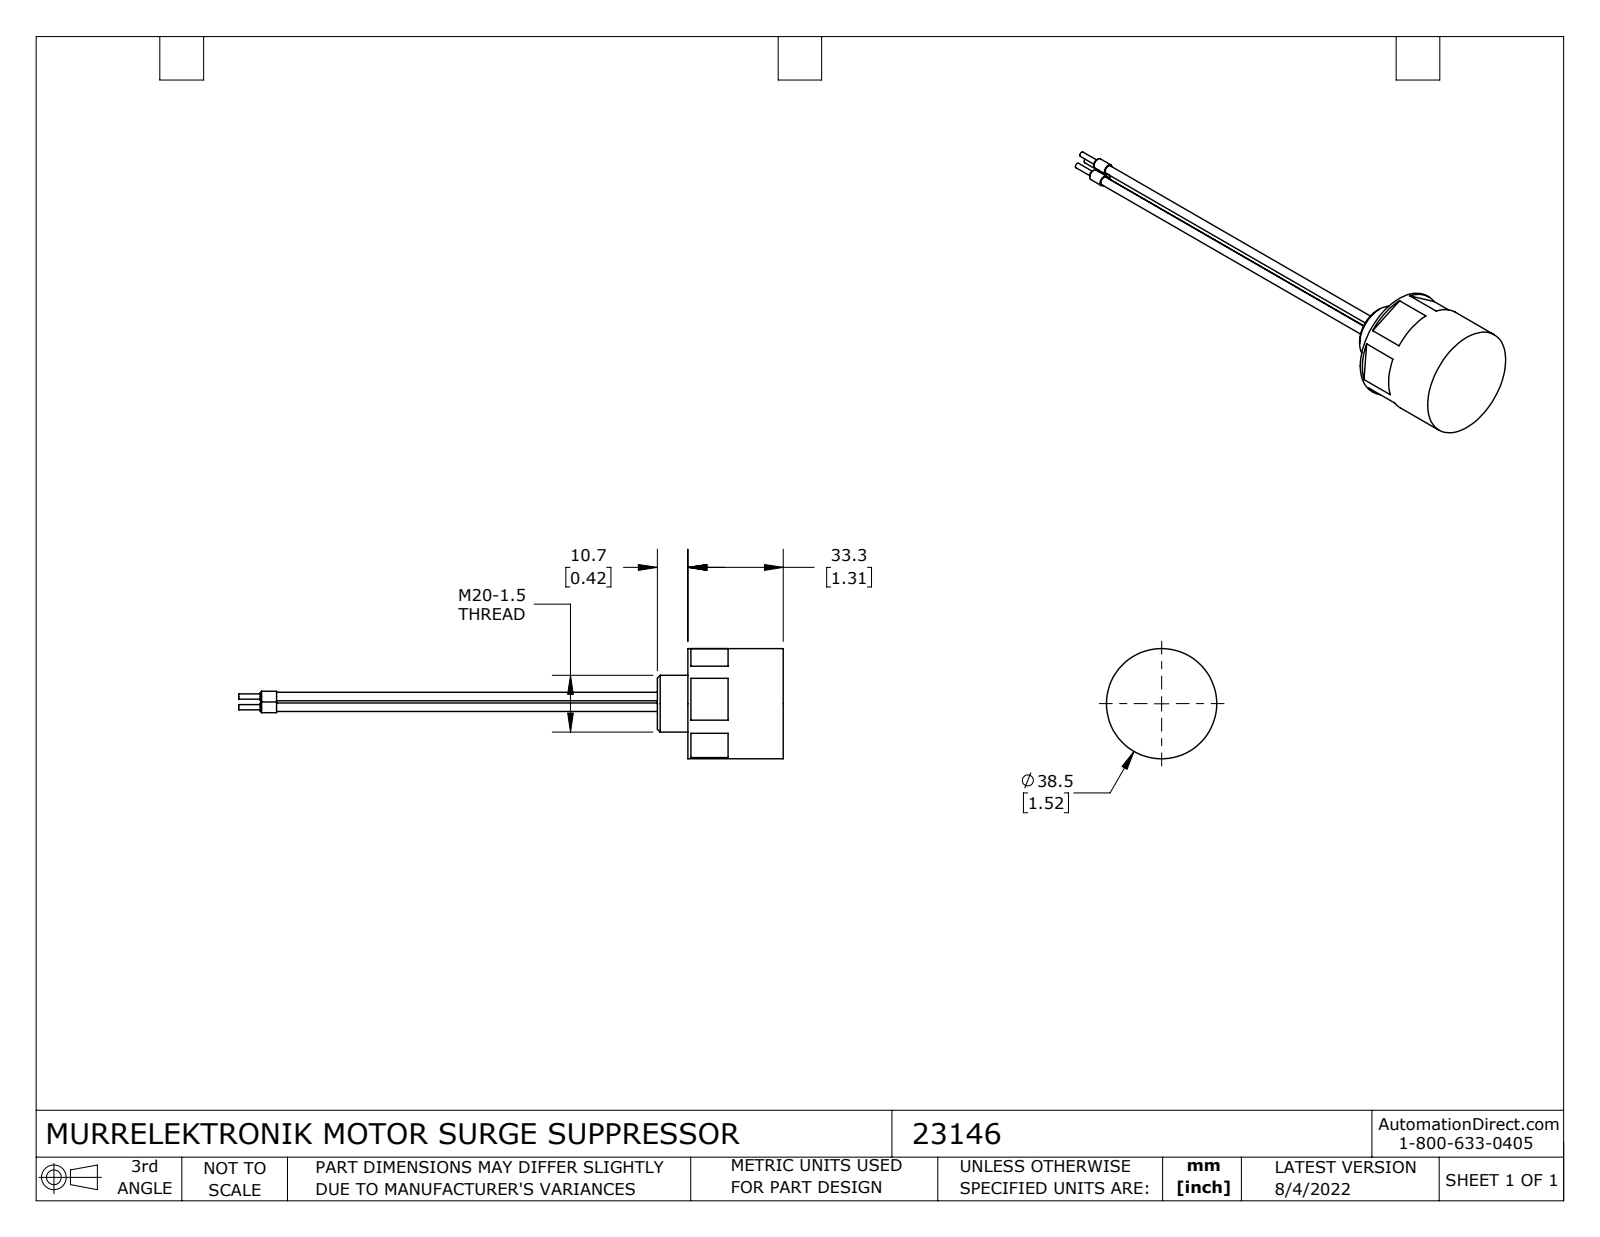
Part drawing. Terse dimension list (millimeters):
name: 23146
written by: SolidWorks 2021 (CONFIG_CONTROL_DESIGN)
unit: mm
bodies: 1 solid, 60 faces (30 planar, 22 cylindrical, 8 other)
size: 190.2 × 38.5 × 38.5
volume: 43 980 mm³; area: 11 230 mm²
bosses: 3× ⌀3.8, 3× ⌀3, 3× ⌀1.8, 1× ⌀38.5, 1× ⌀19.8
face distances: 33.3, 35.6, 44, 10.7, 35.6, 32.3, 1, 11.7, 19.3, 13
